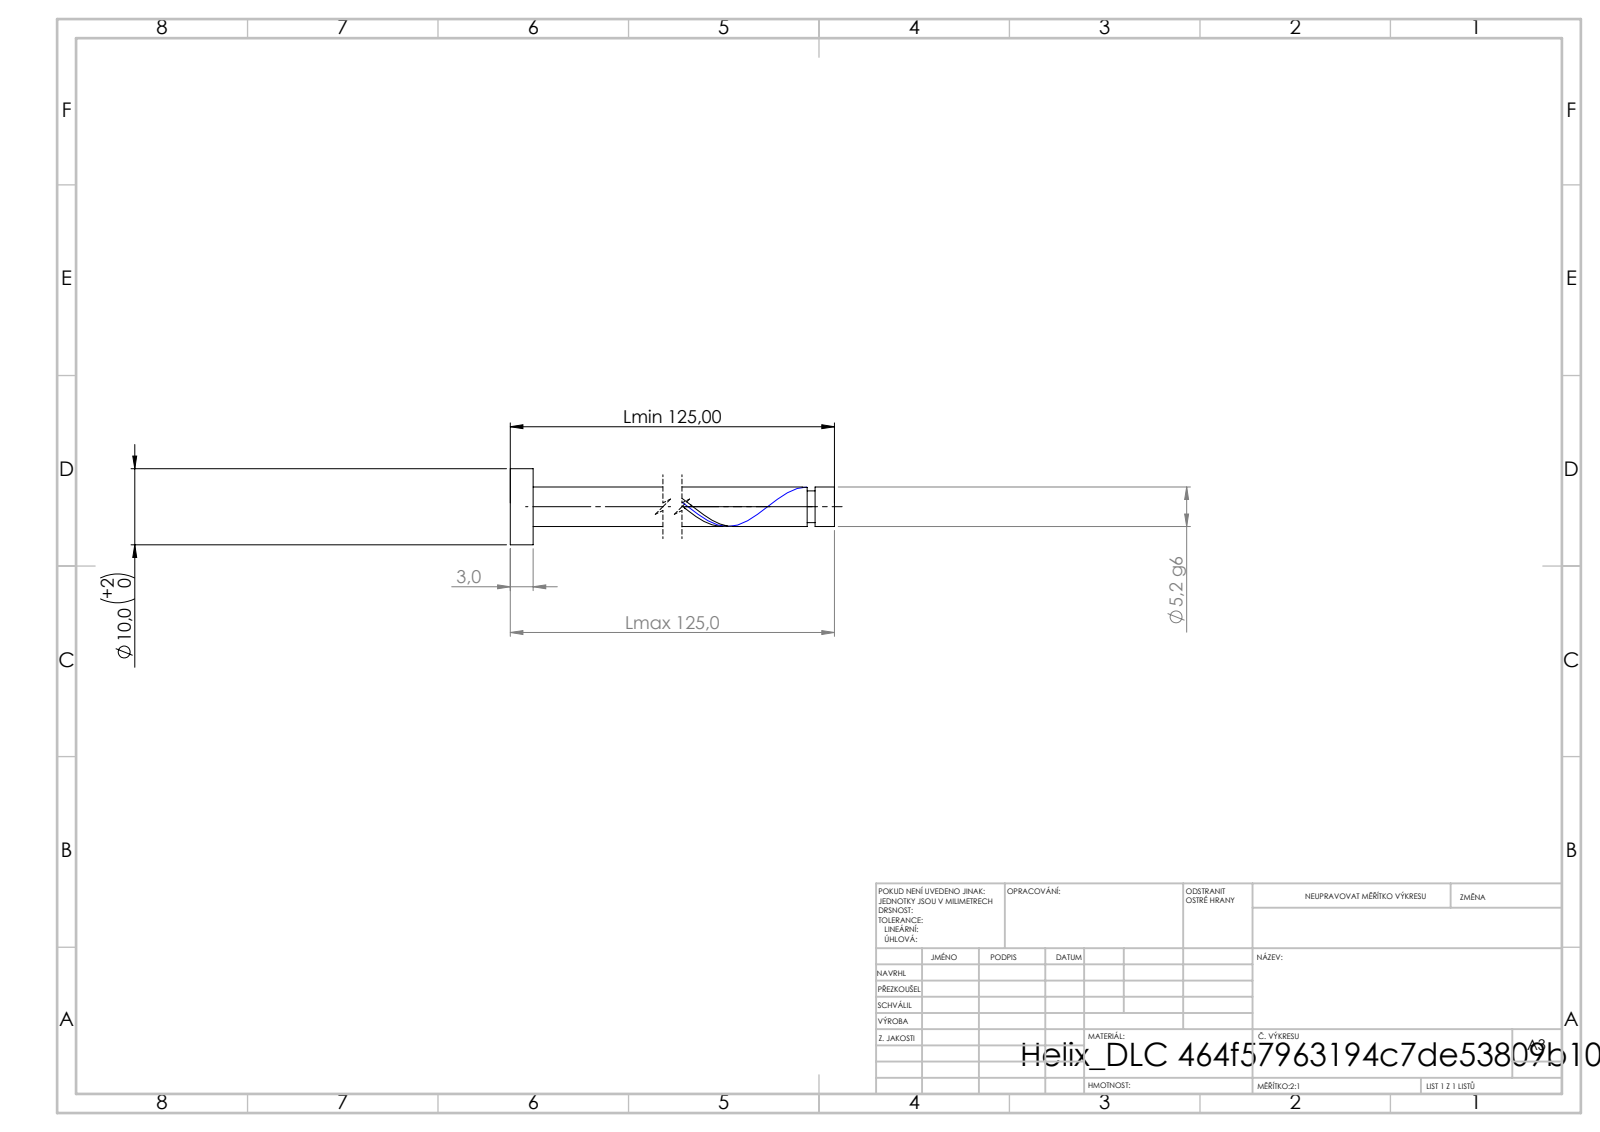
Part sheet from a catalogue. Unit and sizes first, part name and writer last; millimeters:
Units: millimetres
Overall size (bounding box): 125 × 10 × 10
Round bosses / shafts (diameter × count): ⌀10 ×1, ⌀5.2 ×1, ⌀4.16 ×1
Main face-to-face distances: 3, 125, 122, 122.46, 119.46, 2.54, 121.42, 118.42, 1.04, 3.58
Volume: 2 793 mm³ · Surface area: 2 299 mm²
Bodies: 1 solid, 21 faces (6 planar, 14 cylindrical, 1 other)
STEP written by: SolidWorks 2019 (CONFIG_CONTROL_DESIGN)
